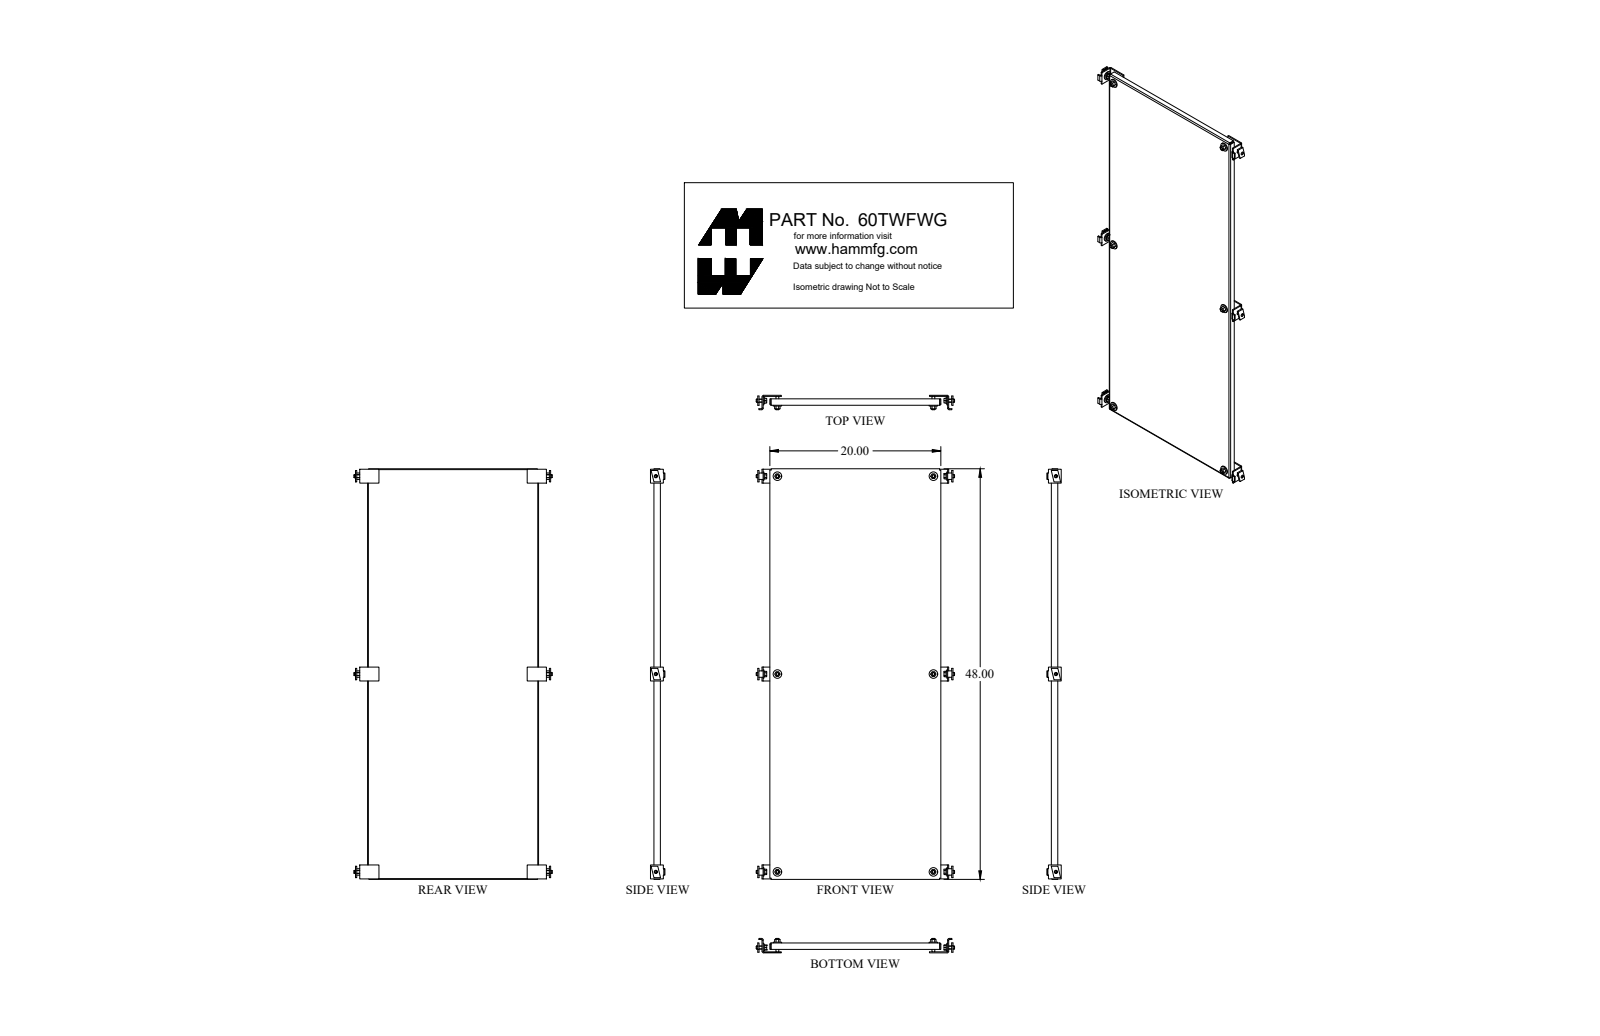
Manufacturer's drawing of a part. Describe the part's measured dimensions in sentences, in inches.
The part is named "60TWFWG_Default". Its 3-D file was written by "SolidWorks 2018 (CONFIG_CONTROL_DESIGN)". It is 13 solids with 270 faces: 130 planar, 92 cylindrical and 48 other. Overall it measures 48 by 22.582 by 1.687 inches. Its volume is 104.5 cubic inches and its surface area 2 193 square inches. Round holes: 6 of diameter 0.563, 3 of diameter 0.437. Round bosses or shafts: 6 of diameter 0.65, 6 of diameter 0.375, 6 of diameter 0.33. Partial cylindrical surfaces (rounded edges, fillets, slot ends): 4 of radius 0.048, 4 of radius 0.06, 4 of radius 0.143, 4 of radius 0.185. The main face-to-face distances are 0.095, 19.905, 0.125, 19.81, 20, 47.905, 1.032, 0.937, 1.157, 1.062. The hole center spacings are 23.125, 29.459, 18.25, 46.25, 49.721, 23.13, 23.13, 46.26.
